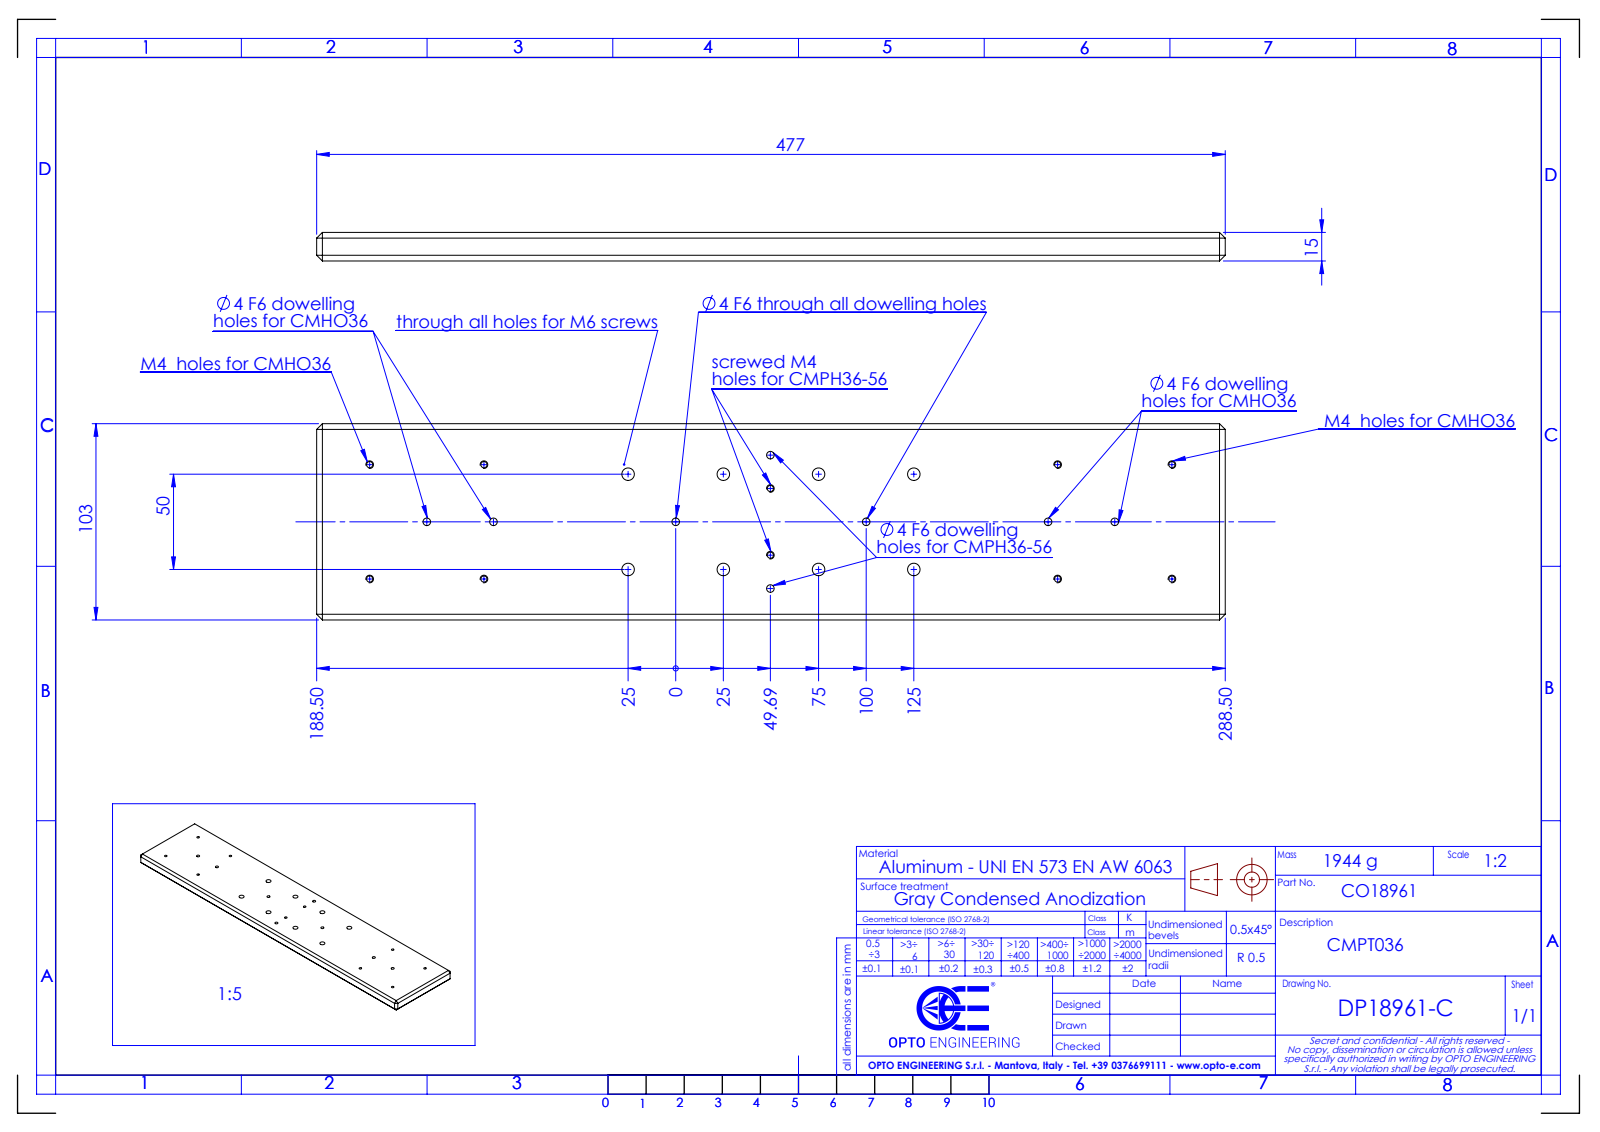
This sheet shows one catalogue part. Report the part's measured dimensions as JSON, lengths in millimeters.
{"part_name": "CMPT", "step_written_by": "SolidWorks 2021 (AUTOMOTIVE_DESIGN)", "units": "millimeters", "bodies": {"solids": 1, "faces": 84, "planar": 32, "cylindrical": 52, "other": 0}, "overall_size": [477, 103, 15], "volume_mm3": 720005, "surface_area_mm2": 115732, "round_holes": [[3.3, 10], [4, 8], [6.6, 8]], "face_to_face_distances": [15, 103, 79.18, 477, 343.6, 5, 405.82, 10, 336.39], "hole_center_spacings": [50, 35.36, 42.43, 60, 70.71, 100, 361.18, 30.41]}
